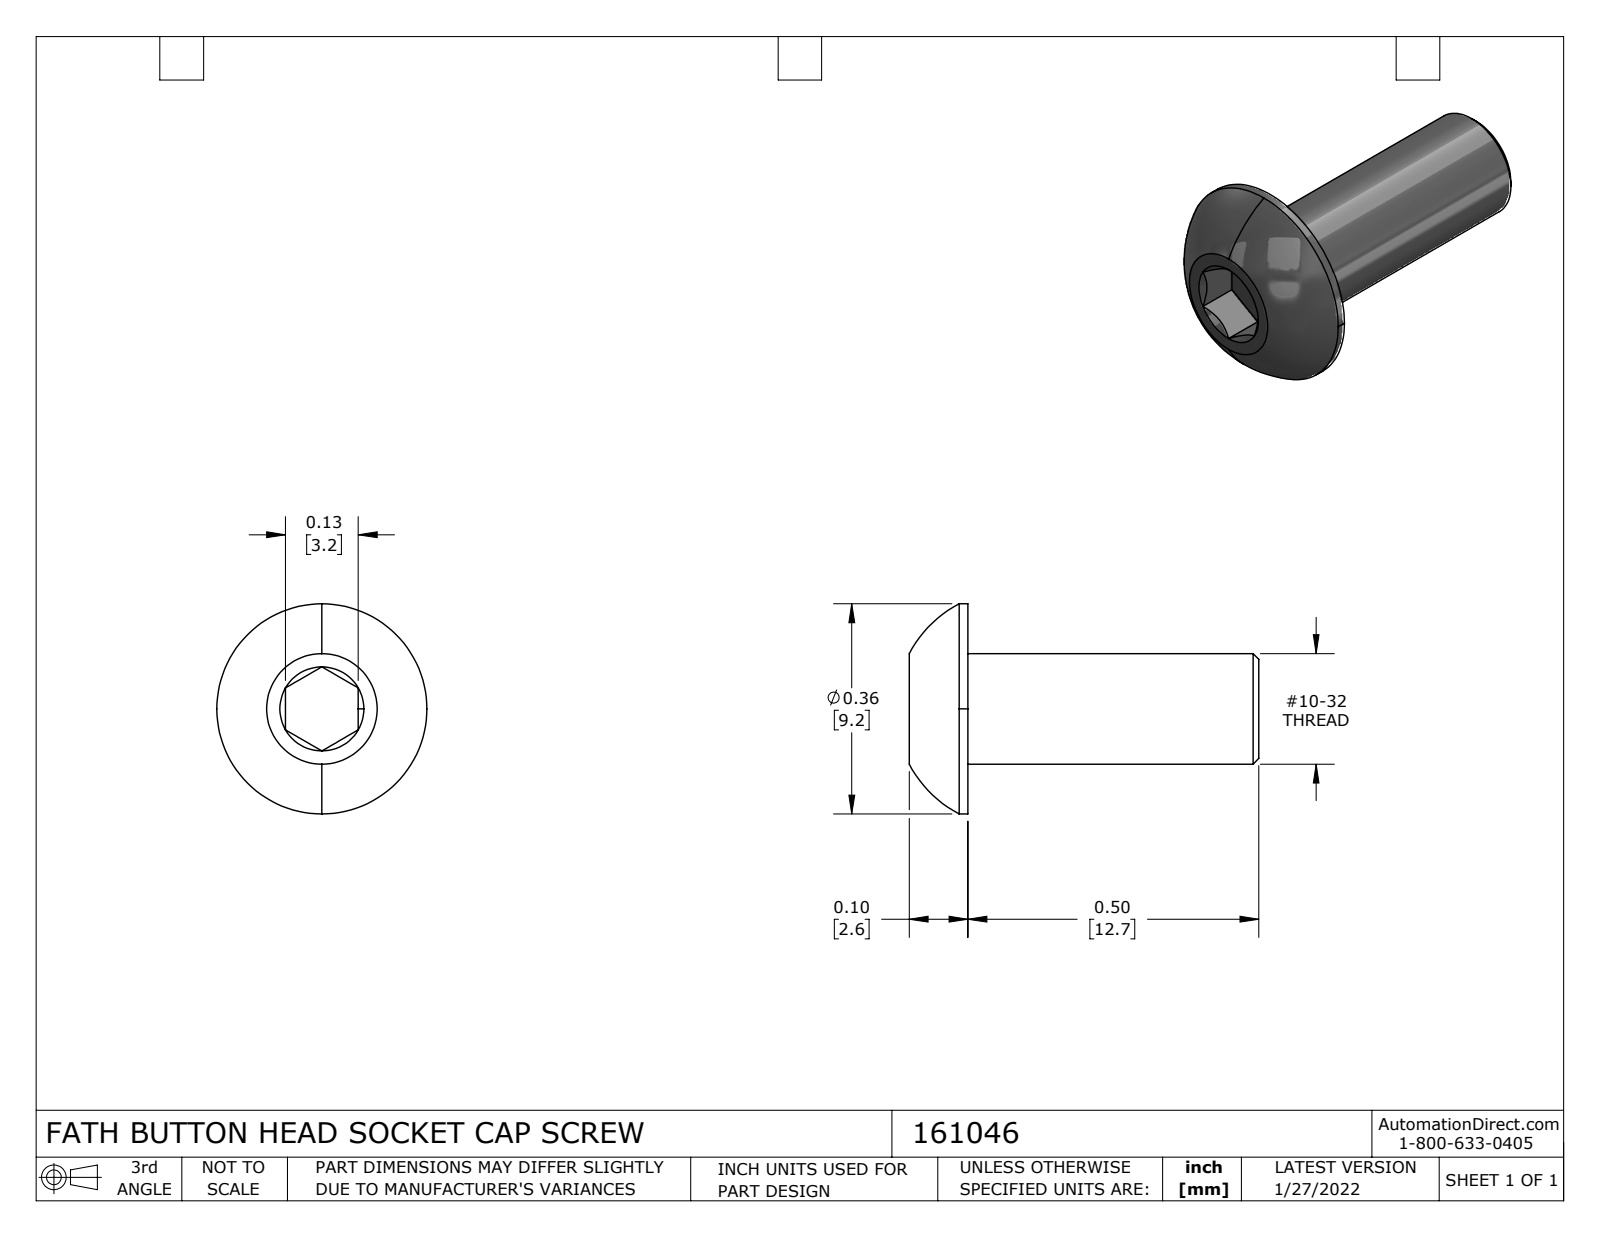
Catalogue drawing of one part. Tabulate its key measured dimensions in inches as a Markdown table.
| quantity | value |
| --- | --- |
| part name | 161046 |
| STEP written by | SolidWorks 2021 (CONFIG_CONTROL_DESIGN) |
| units | inches |
| bodies | 1 solid, 29 faces (12 planar, 4 cylindrical, 13 other) |
| overall size | 0.601 × 0.361 × 0.361 |
| volume | 0.021 in³ |
| surface area | 0.582 in² |
| round bosses / shafts (diameter × count) | 0.361 × 1, 0.19 × 1 |
| main face-to-face distances | 0.5, 0.125, 0.53, 0.03, 0.601, 0.101, 0.071, 0.063 |
